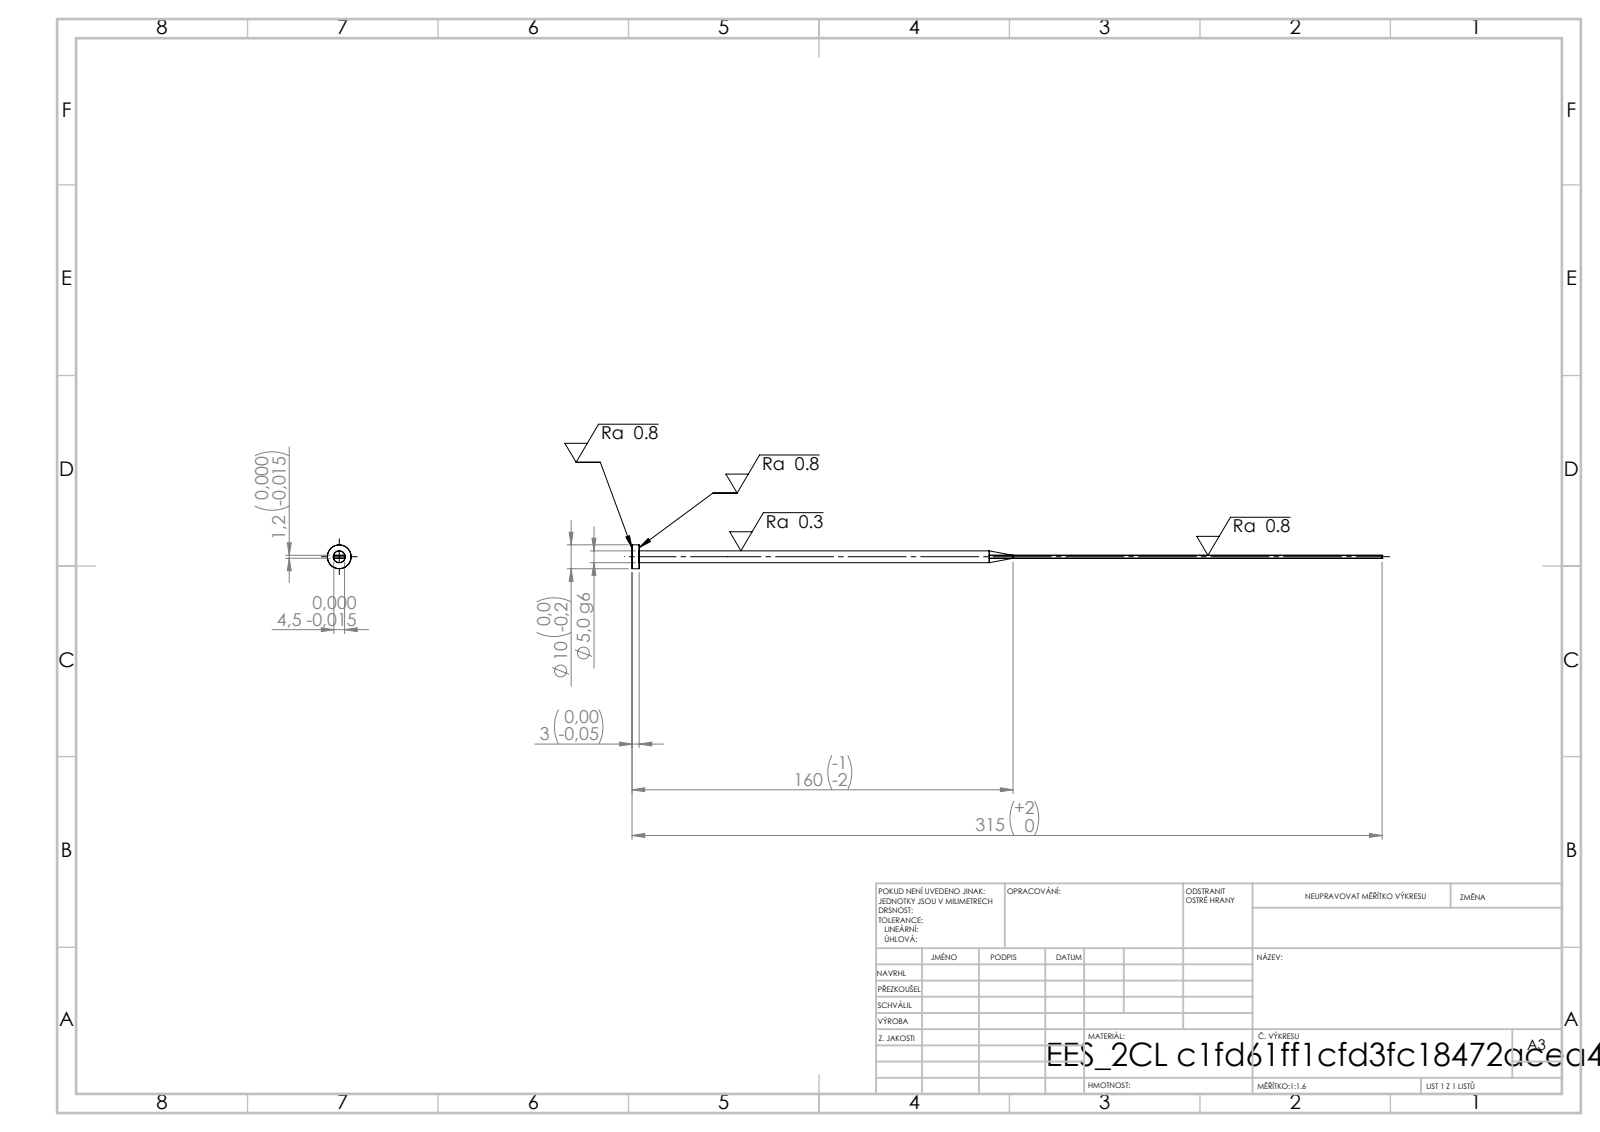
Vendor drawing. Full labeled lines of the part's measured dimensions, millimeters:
STEP written by: SolidWorks 2019 (CONFIG_CONTROL_DESIGN)
Units: millimetres
Bodies: 1 solid, 15 faces (7 planar, 4 cylindrical, 4 other)
Overall size (bounding box): 315 × 10 × 10
Volume: 4 079 mm³ · Surface area: 4 444 mm²
Round bosses / shafts (diameter × count): ⌀10 ×1, ⌀5 ×1
Main face-to-face distances: 1.2, 4.5, 3, 315, 312
